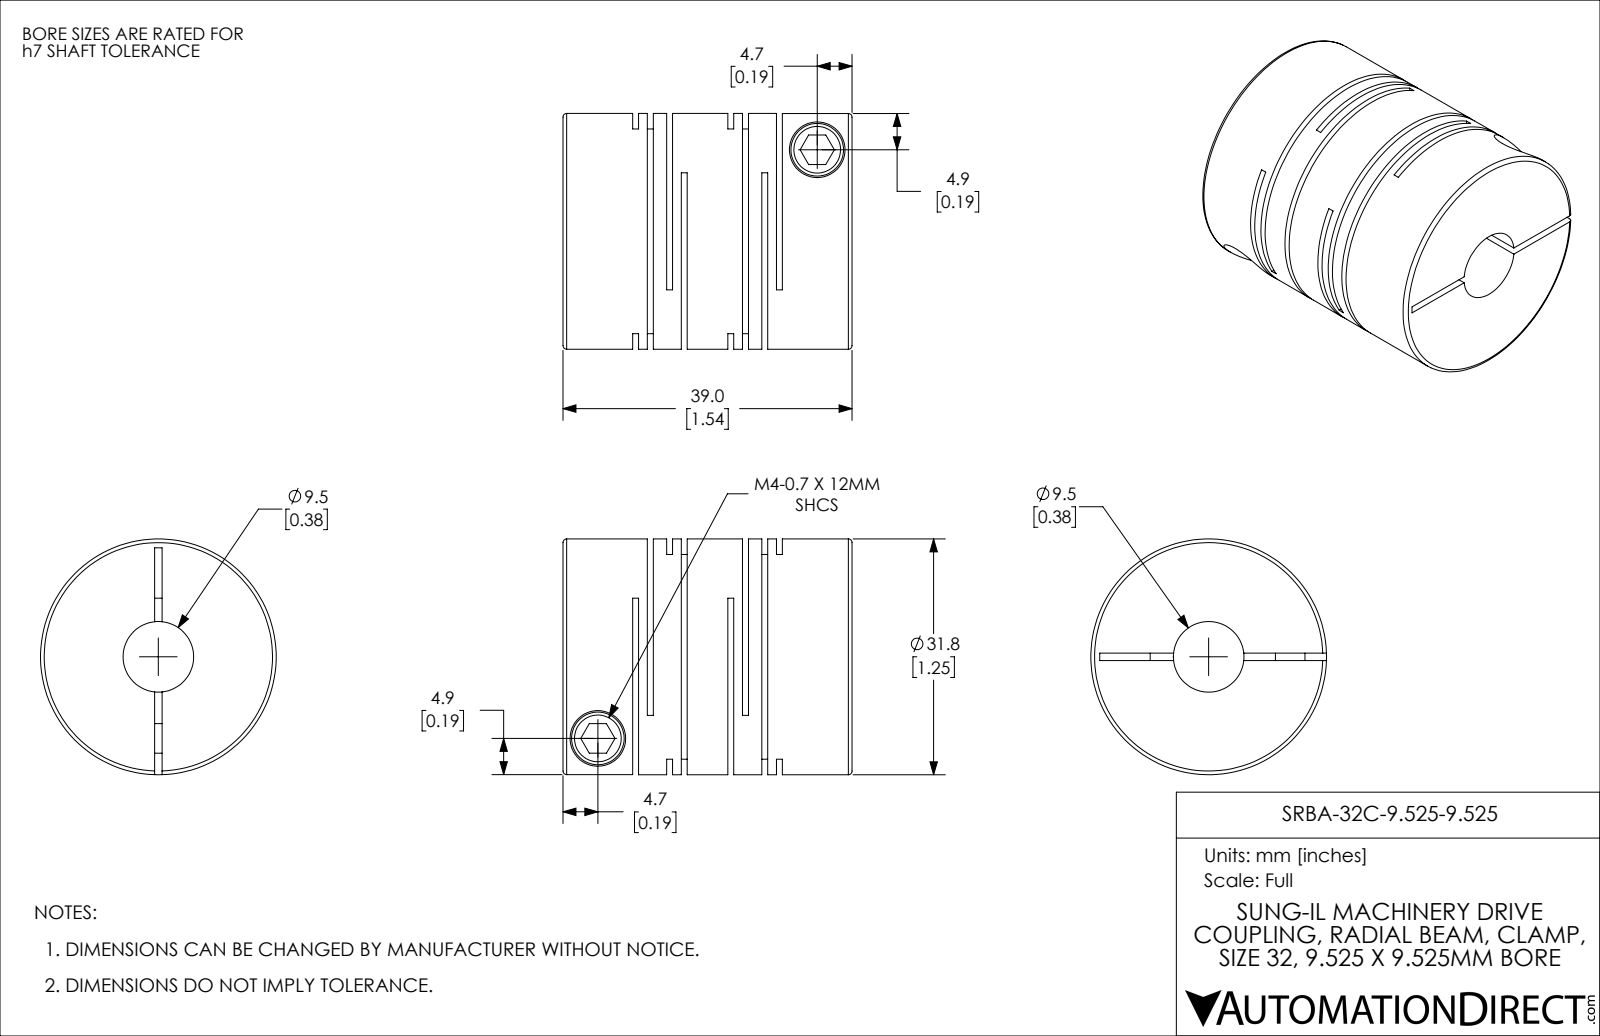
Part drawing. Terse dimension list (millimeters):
name: SRBA-32C-9.525-9.525
written by: SolidWorks 2021 (CONFIG_CONTROL_DESIGN)
unit: mm
bodies: 1 solid, 114 faces (60 planar, 42 cylindrical, 12 other)
size: 39 × 31.8 × 31.8
volume: 23 678 mm³; area: 16 307 mm²
holes: 2× ⌀4, 2× ⌀7.5, 1× ⌀9.53
bosses: 2× ⌀7.1, 1× ⌀31.8
face distances: 0.8, 1.98, 12.84, 4.58, 12.04, 1.18, 10.86, 3.78, 8.26, 2.6
